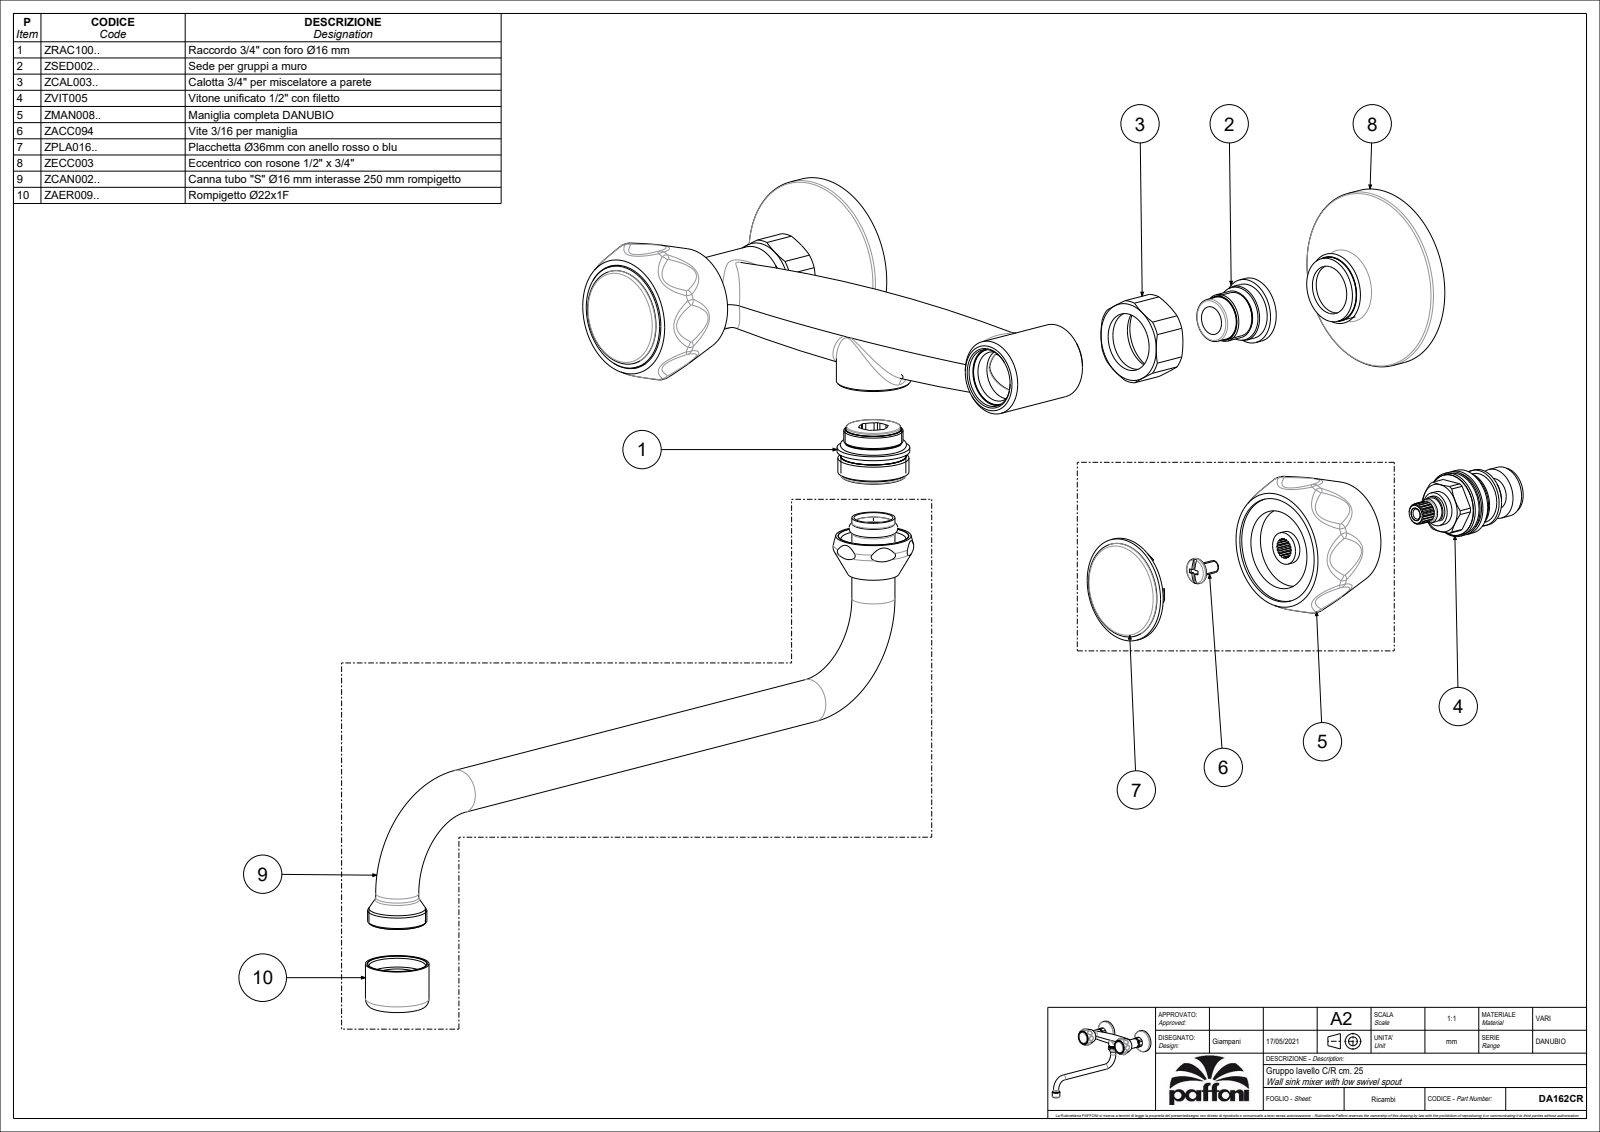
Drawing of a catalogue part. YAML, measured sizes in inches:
part_name: "DA162CR"
step_written_by: "CREO PARAMETRIC BY PTC INC, 2020044 (CONFIG_CONTROL_DESIGN)"
units: inches
bodies: {solids: 3, faces: 513, planar: 91, cylindrical: 150, other: 272}
overall_size: [12.394, 8.819, 6.689]
volume: 16.09
surface_area: 168.6
round_holes:
  - {diameter: 0.65, count: 3}
  - {diameter: 0.846, count: 3}
  - {diameter: 0.945, count: 3}
  - {diameter: 0.732, count: 2}
  - {diameter: 0.748, count: 2}
  - {diameter: 0.949, count: 2}
  - {diameter: 1.051, count: 2}
  - {diameter: 2.52, count: 2}
  - {diameter: 0.449, count: 1}
  - {diameter: 0.567, count: 1}
  - {diameter: 0.673, count: 1}
  - {diameter: 0.807, count: 1}
round_bosses_or_shafts:
  - {diameter: 1.083, count: 3}
  - {diameter: 1.063, count: 3}
  - {diameter: 0.63, count: 3}
  - {diameter: 2.598, count: 2}
  - {diameter: 1.516, count: 2}
  - {diameter: 0.929, count: 1}
  - {diameter: 0.866, count: 1}
  - {diameter: 0.799, count: 1}
partial_cylinders:
  - {radius: 0.839, count: 16}
  - {radius: 0.61, count: 2}
  - {radius: 0.207, count: 1}
face_to_face_distances: [2.748, 2.743, 1.142, 1.39, 1.299, 3.11, 1.294, 1.449, 0.157, 4.138]
hole_center_spacings: [6.22]
